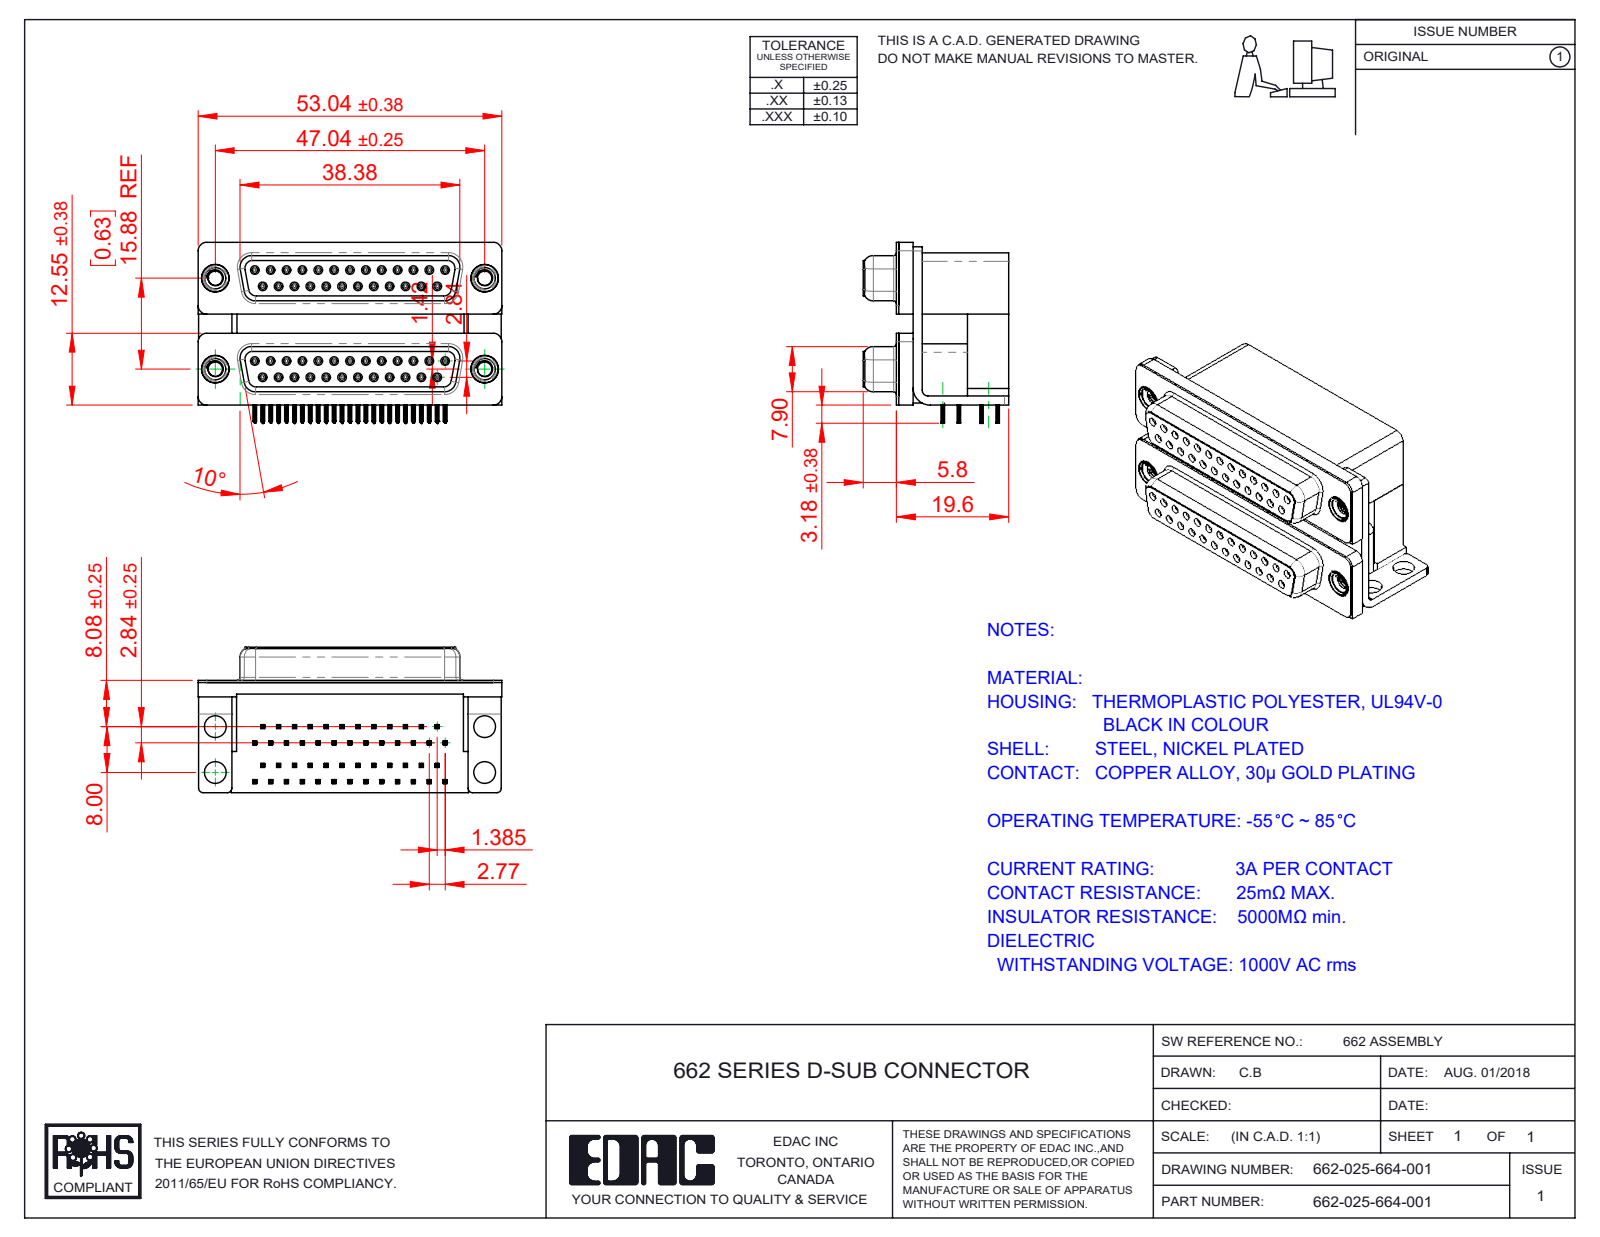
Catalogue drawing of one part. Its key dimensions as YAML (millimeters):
part_name: "662 Housing Lower_25 Contacts; 662 Threaded Rivet_M3; 662-025-664-001; 662 Contact Top Lower (+7 more)"
step_written_by: "SolidWorks 2020 (CONFIG_CONTROL_DESIGN)"
units: millimeters
bodies: {solids: 61, faces: 7796, planar: 3576, cylindrical: 1812, other: 2408}
overall_size: [53.04, 31.61, 25.4]
volume: 22866
surface_area: 24947
round_holes:
  - {diameter: 0.8, count: 50}
  - {diameter: 0.9, count: 50}
  - {diameter: 2.5, count: 4}
  - {diameter: 3.5, count: 4}
  - {diameter: 3.8, count: 4}
  - {diameter: 4, count: 4}
  - {diameter: 4.8, count: 4}
  - {diameter: 5, count: 4}
round_bosses_or_shafts:
  - {diameter: 1.2, count: 50}
  - {diameter: 4.9, count: 4}
  - {diameter: 4.75, count: 4}
  - {diameter: 3.9, count: 4}
partial_cylinders:
  - {radius: 0.1, count: 400}
  - {radius: 0.15, count: 200}
  - {radius: 0.35, count: 100}
  - {radius: 0.34, count: 50}
  - {radius: 0.28, count: 24}
  - {radius: 1.35, count: 18}
  - {radius: 1.5, count: 13}
  - {radius: 0.5, count: 8}
face_to_face_distances: [15.88, 19.2, 0.4, 7.2, 12, 10.7, 6.2, 16.7, 9.5, 2.5]
hole_center_spacings: [3.16, 2.77, 5.54, 11.08, 8.31, 5.03, 13.85, 7.48]
